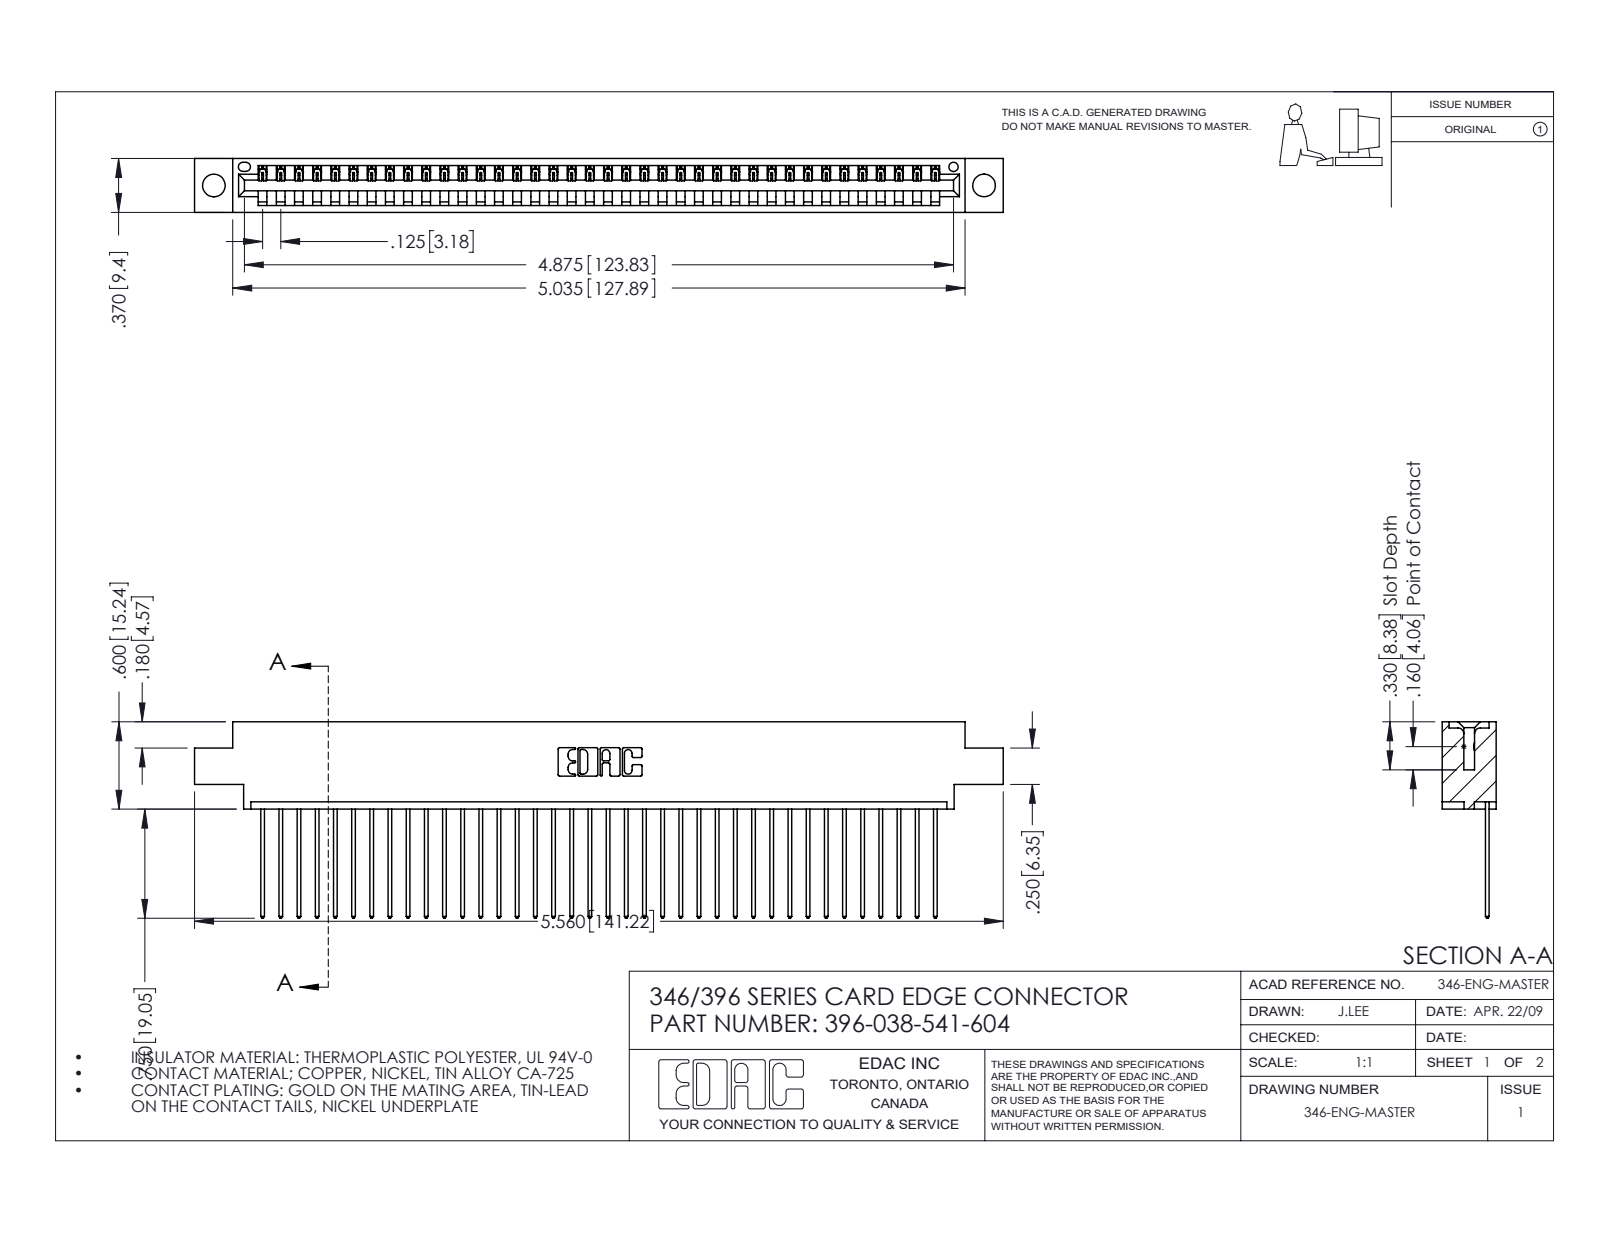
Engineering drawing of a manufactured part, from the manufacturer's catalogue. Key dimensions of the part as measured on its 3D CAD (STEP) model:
Part name (STEP PRODUCT): 346 Part_0.170 Offset - 0.156 Dia-TH; 345-292-001_345-293-141; 396-038-541-604
STEP written by: SolidWorks 2016 (CONFIG_CONTROL_DESIGN)
Units: inches
Bodies: 39 solids, 2330 faces (1600 planar, 730 cylindrical, 0 other)
Overall size (bounding box): 5.56 × 1.35 × 0.37
Volume: 0.816 in³ · Surface area: 26.95 in²
Round holes (diameter × count): ⌀0.156 ×2, ⌀0.064 ×1
Partial cylindrical surfaces — rounded edges, fillets, slot ends (radius × count): R0.006 ×76, R0.01 ×76, R0.01 ×22, R0.007 ×6, R0.031 ×6, R0.026 ×3, R0.031 ×2, R0.04 ×2
Main face-to-face distances: 0.048, 0.322, 0.37, 0.25, 0.072, 0.298, 0.025, 0.148, 0.222, 0.1
Hole centre spacings: 0.246, 5.086, 5.295
